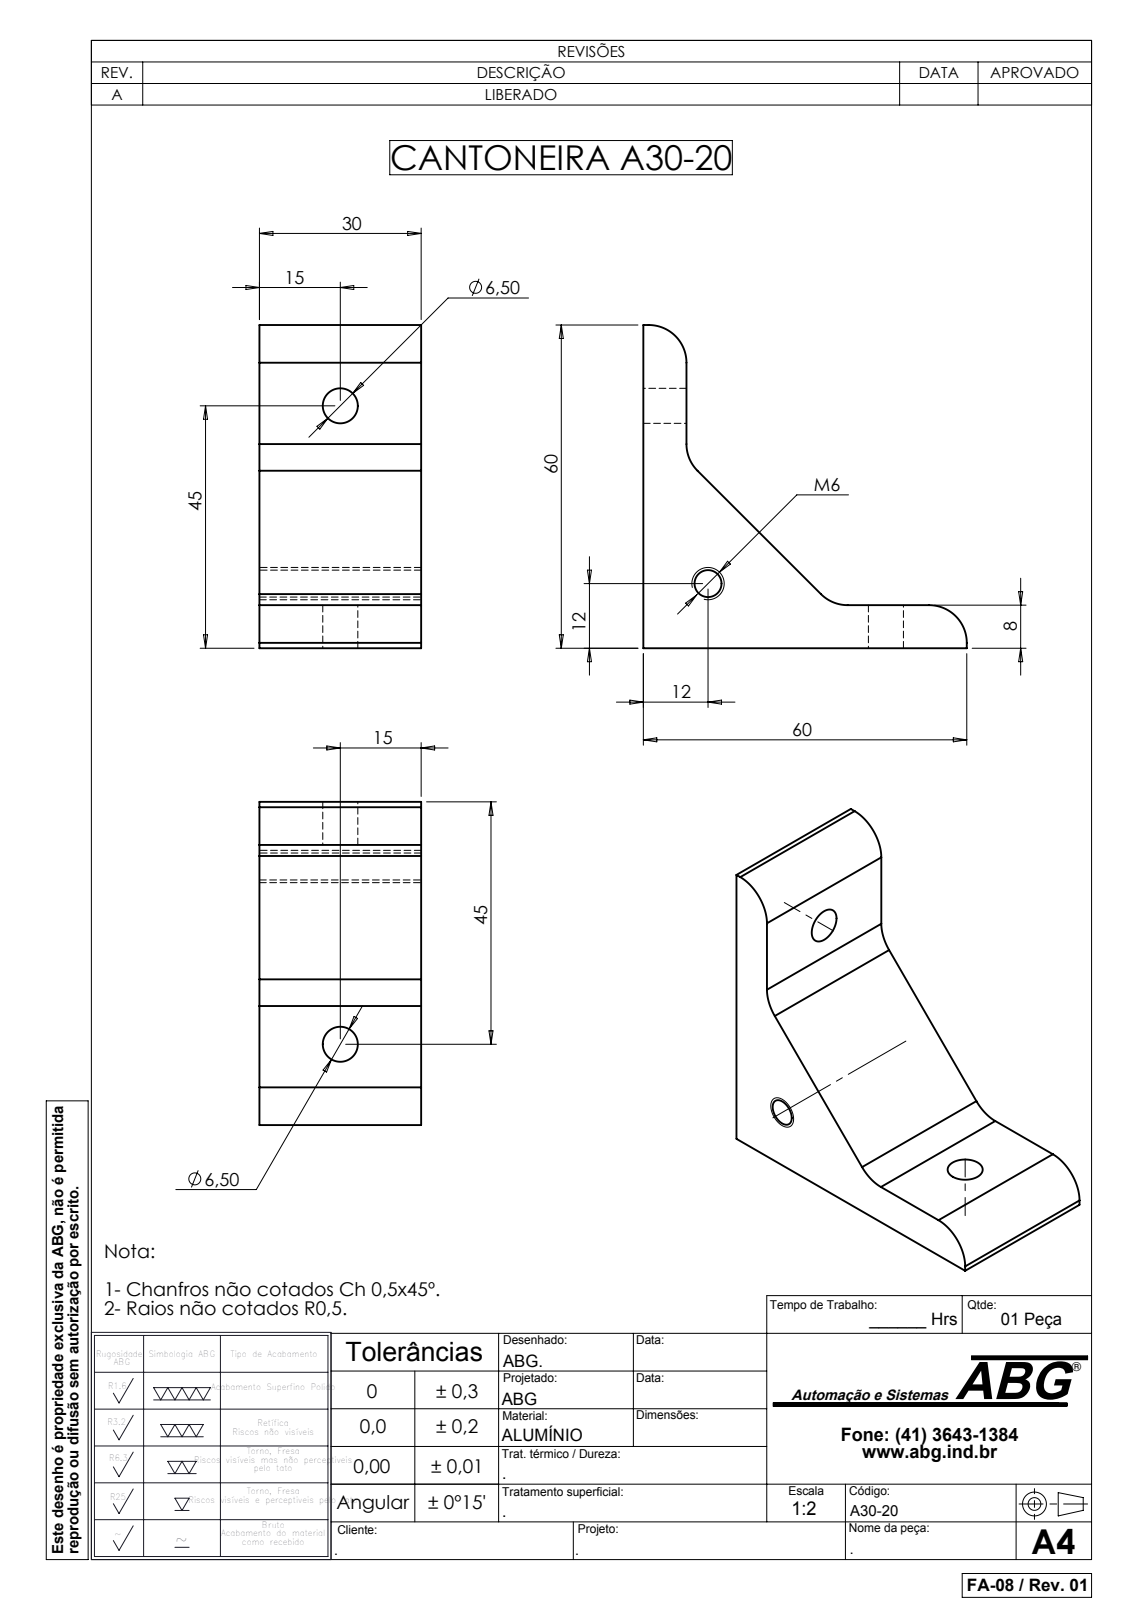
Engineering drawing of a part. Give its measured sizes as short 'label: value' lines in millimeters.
name: A30-20
written by: SolidWorks 2007 (CONFIG_CONTROL_DESIGN)
unit: mm
bodies: 1 solid, 19 faces (9 planar, 10 cylindrical, 0 other)
size: 60 × 60 × 30
volume: 36 127 mm³; area: 9 636 mm²
holes: 2× ⌀6.5, 1× ⌀5
rounds: 4× R7
face distances: 30, 8, 60, 52
